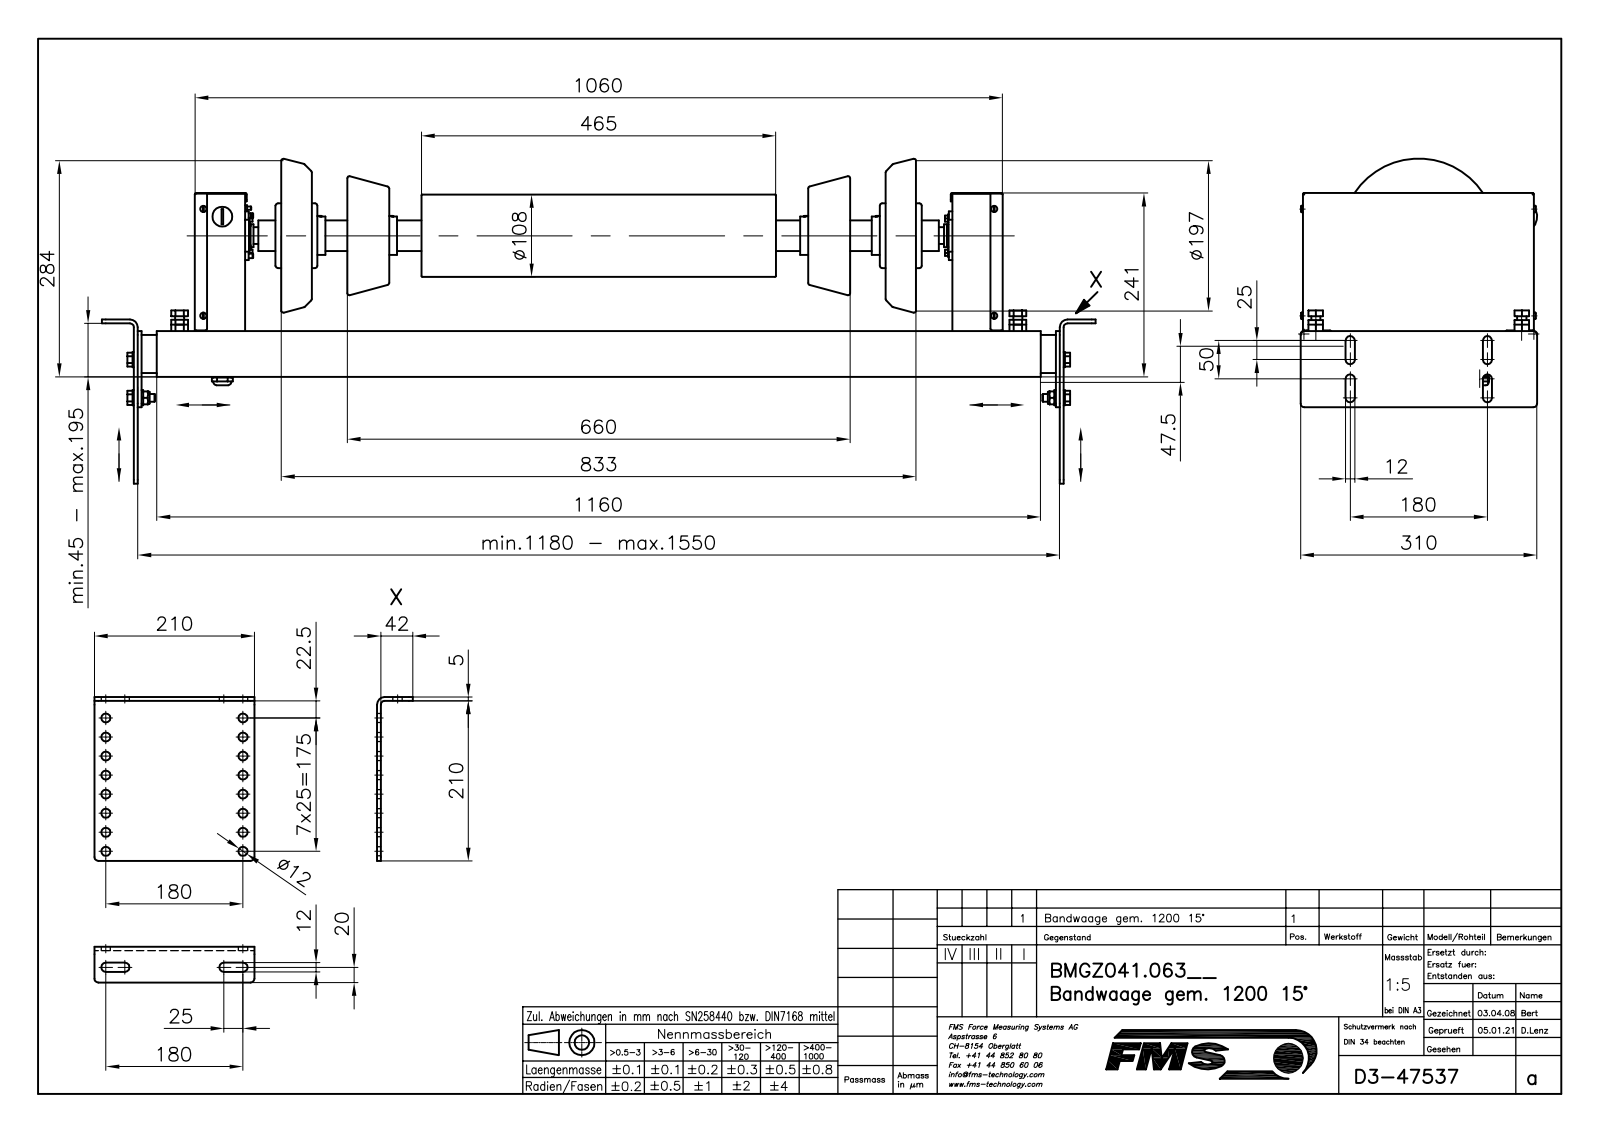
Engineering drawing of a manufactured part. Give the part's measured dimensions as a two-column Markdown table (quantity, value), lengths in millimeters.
| quantity | value |
| --- | --- |
| part name | B47537_STP; B50109; 6KT-SCHRAUBE_M12X30; ZYL_SCHR__M4X8 (+8 more) |
| STEP written by | Mechanical Desktop 2009 (CONFIG_CONTROL_DESIGN) |
| units | millimeters |
| bodies | 179 solids, 2932 faces (1427 planar, 1058 cylindrical, 447 other) |
| overall size | 1304 × 426.14 × 310.2 |
| volume | 8 553 000 mm³ |
| surface area | 3 714 000 mm² |
| round holes (diameter × count) | 12 × 17, 5 × 6, 3.5 × 4, 4.9 × 4, 6.4 × 4, 6.91 × 4, 8.68 × 4, 8.75 × 4, 10 × 4, 10.5 × 4, 10.68 × 4, 14.8 × 4 |
| round bosses / shafts (diameter × count) | 12 × 11, 8.2 × 8, 4.2 × 8, 20 × 6, 10 × 6, 8 × 6, 5 × 5, 16 × 4 |
| partial cylindrical surfaces (radius × count) | 2 × 34, 1 × 24, 4 × 16, 5 × 16, 6 × 12, 3.5 × 8, 2.25 × 6, 0.5 × 4 |
| main face-to-face distances | 4, 5, 1, 270, 36, 3, 266, 32, 66, 65 |
| hole center spacings | 25, 181.73, 50, 186.82, 75, 195, 100, 180 |
